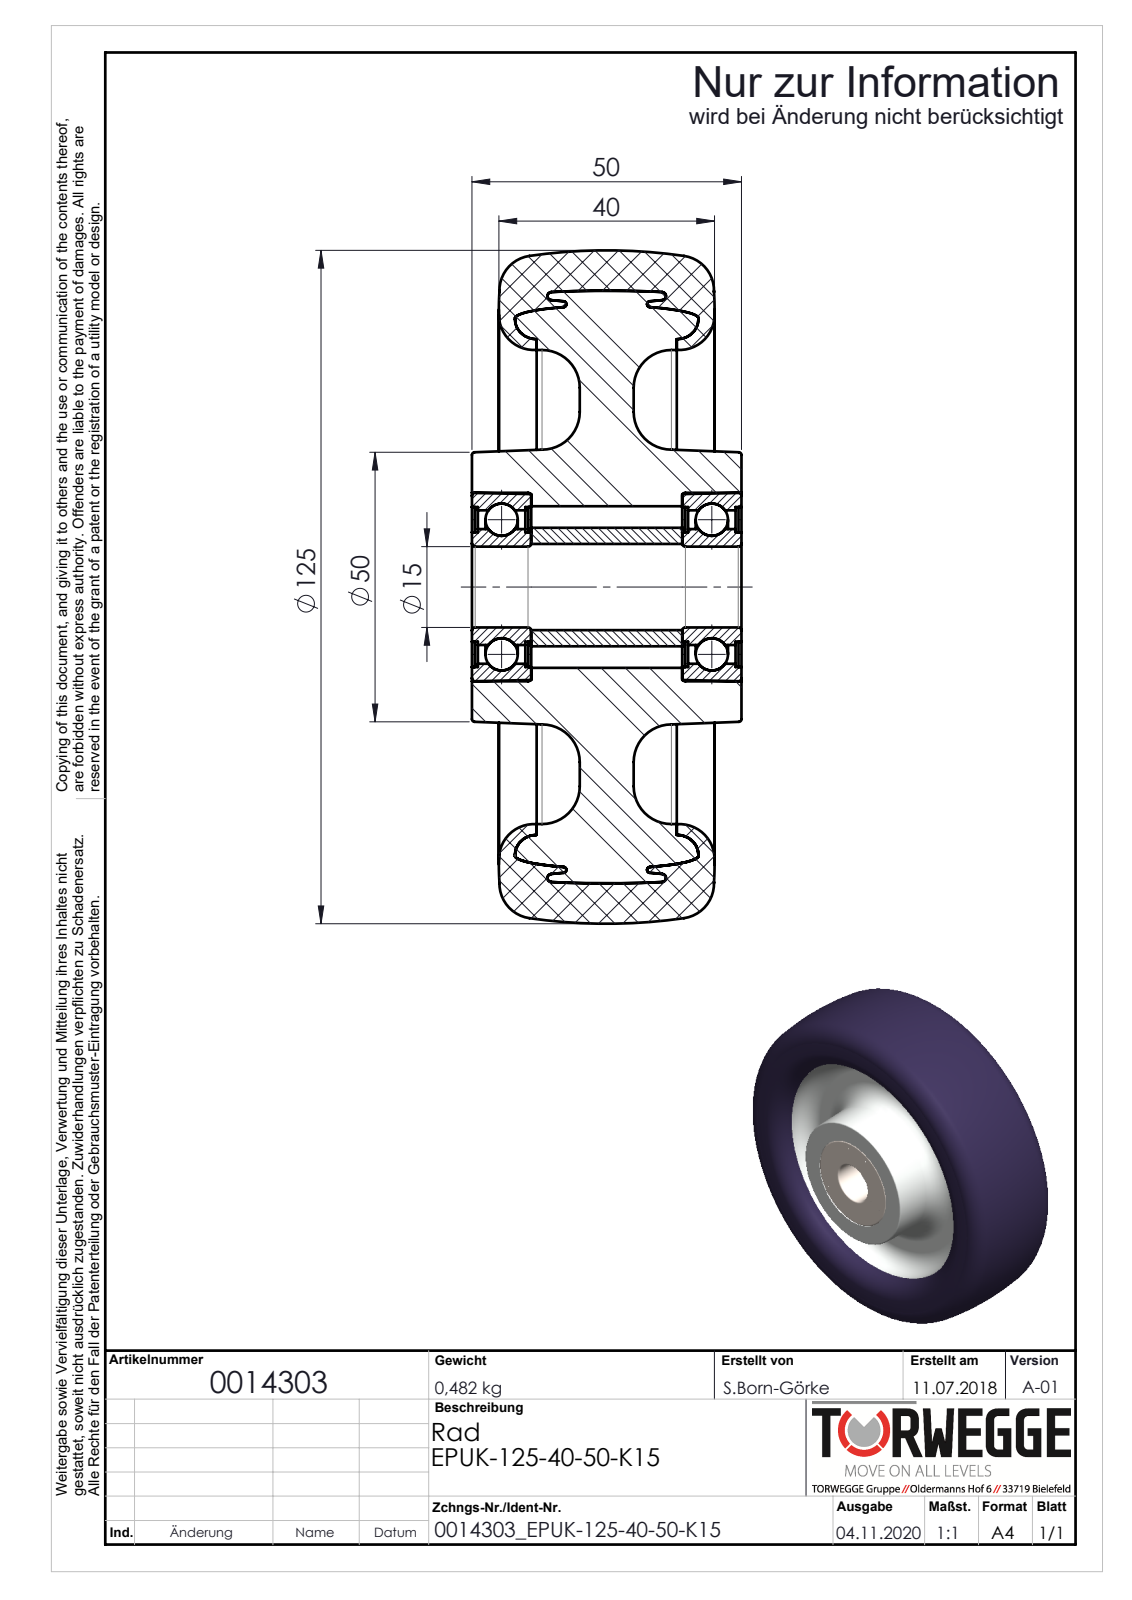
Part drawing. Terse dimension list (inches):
name: 0014303
written by: SolidWorks 2018 (AUTOMOTIVE_DESIGN)
unit: in
bodies: 12 solids, 286 faces (66 planar, 78 cylindrical, 142 other)
size: 4.921 × 4.921 × 1.969
volume: 21.77 in³; area: 110 in²
holes: 1× ⌀0.591, 1× ⌀0.63, 1× ⌀0.799, 1× ⌀1.121, 1× ⌀1.169, 1× ⌀1.181, 1× ⌀3.465
bosses: 1× ⌀2.008, 1× ⌀1.378, 1× ⌀0.866, 1× ⌀0.847
rounds: 1× R2.047
face distances: 1.535, 0.787, 1.181, 0.022, 0.433, 0.354, 0.748, 1.969, 0.411, 0.39
